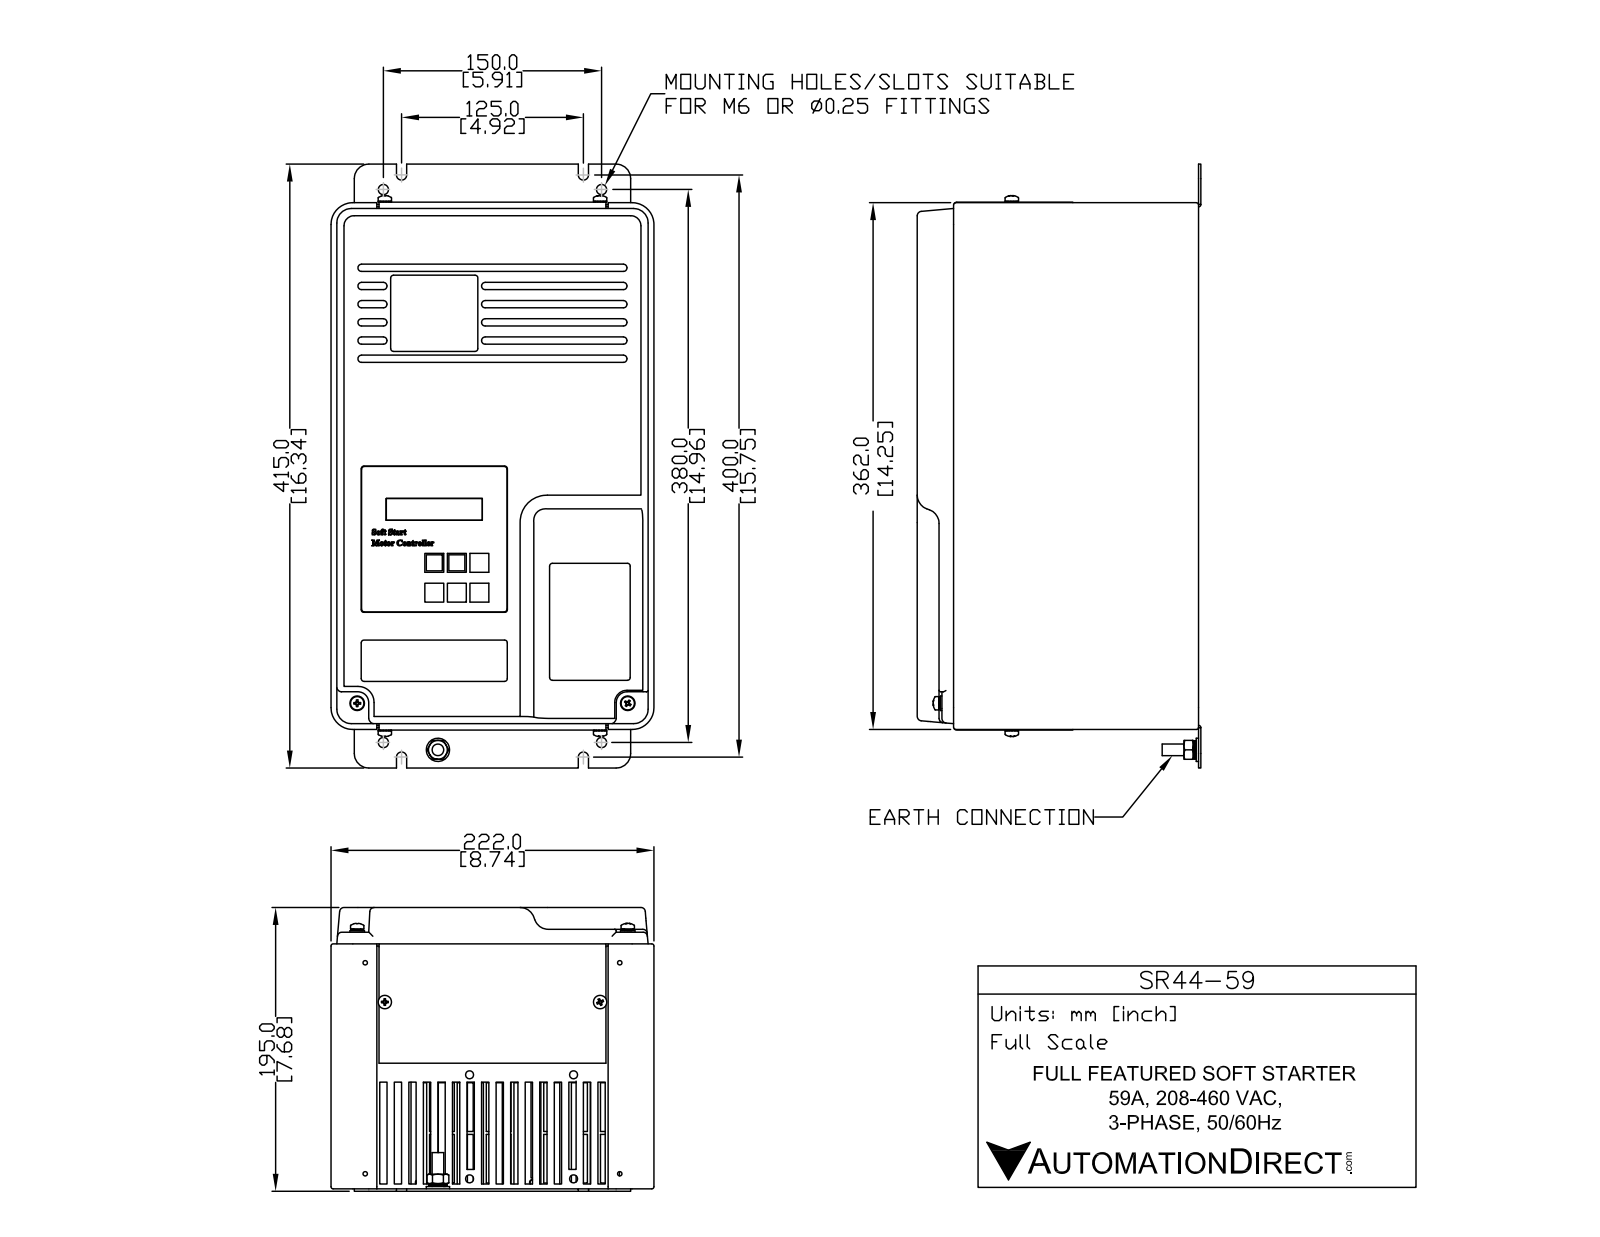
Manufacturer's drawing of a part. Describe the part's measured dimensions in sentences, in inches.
The part is named "SR44-59". Its 3-D file was written by "SolidWorks 2013 (AUTOMOTIVE_DESIGN)". It is 1 solid with 768 faces: 455 planar, 175 cylindrical and 138 other. Overall it measures 16.339 by 8.74 by 7.665 inches. Its volume is 502.3 cubic inches and its surface area 1 102 square inches. Round holes: 4 of diameter 0.276. Round bosses or shafts: 4 of diameter 0.394, 1 of diameter 0.63, 1 of diameter 0.315. Partial cylindrical surfaces (rounded edges, fillets, slot ends): 30 of radius 0.098, 28 of radius 0.094, 12 of radius 0.098, 11 of radius 0.059, 8 of radius 0.118, 8 of radius 0.394, 6 of radius 0.079, 4 of radius 0.138. The main face-to-face distances are 0.401, 0.802, 1.204, 1.605, 2.006, 2.407, 2.808, 0.232, 3.209, 8.508. The hole center spacings are 5.906, 14.961, 16.084.
